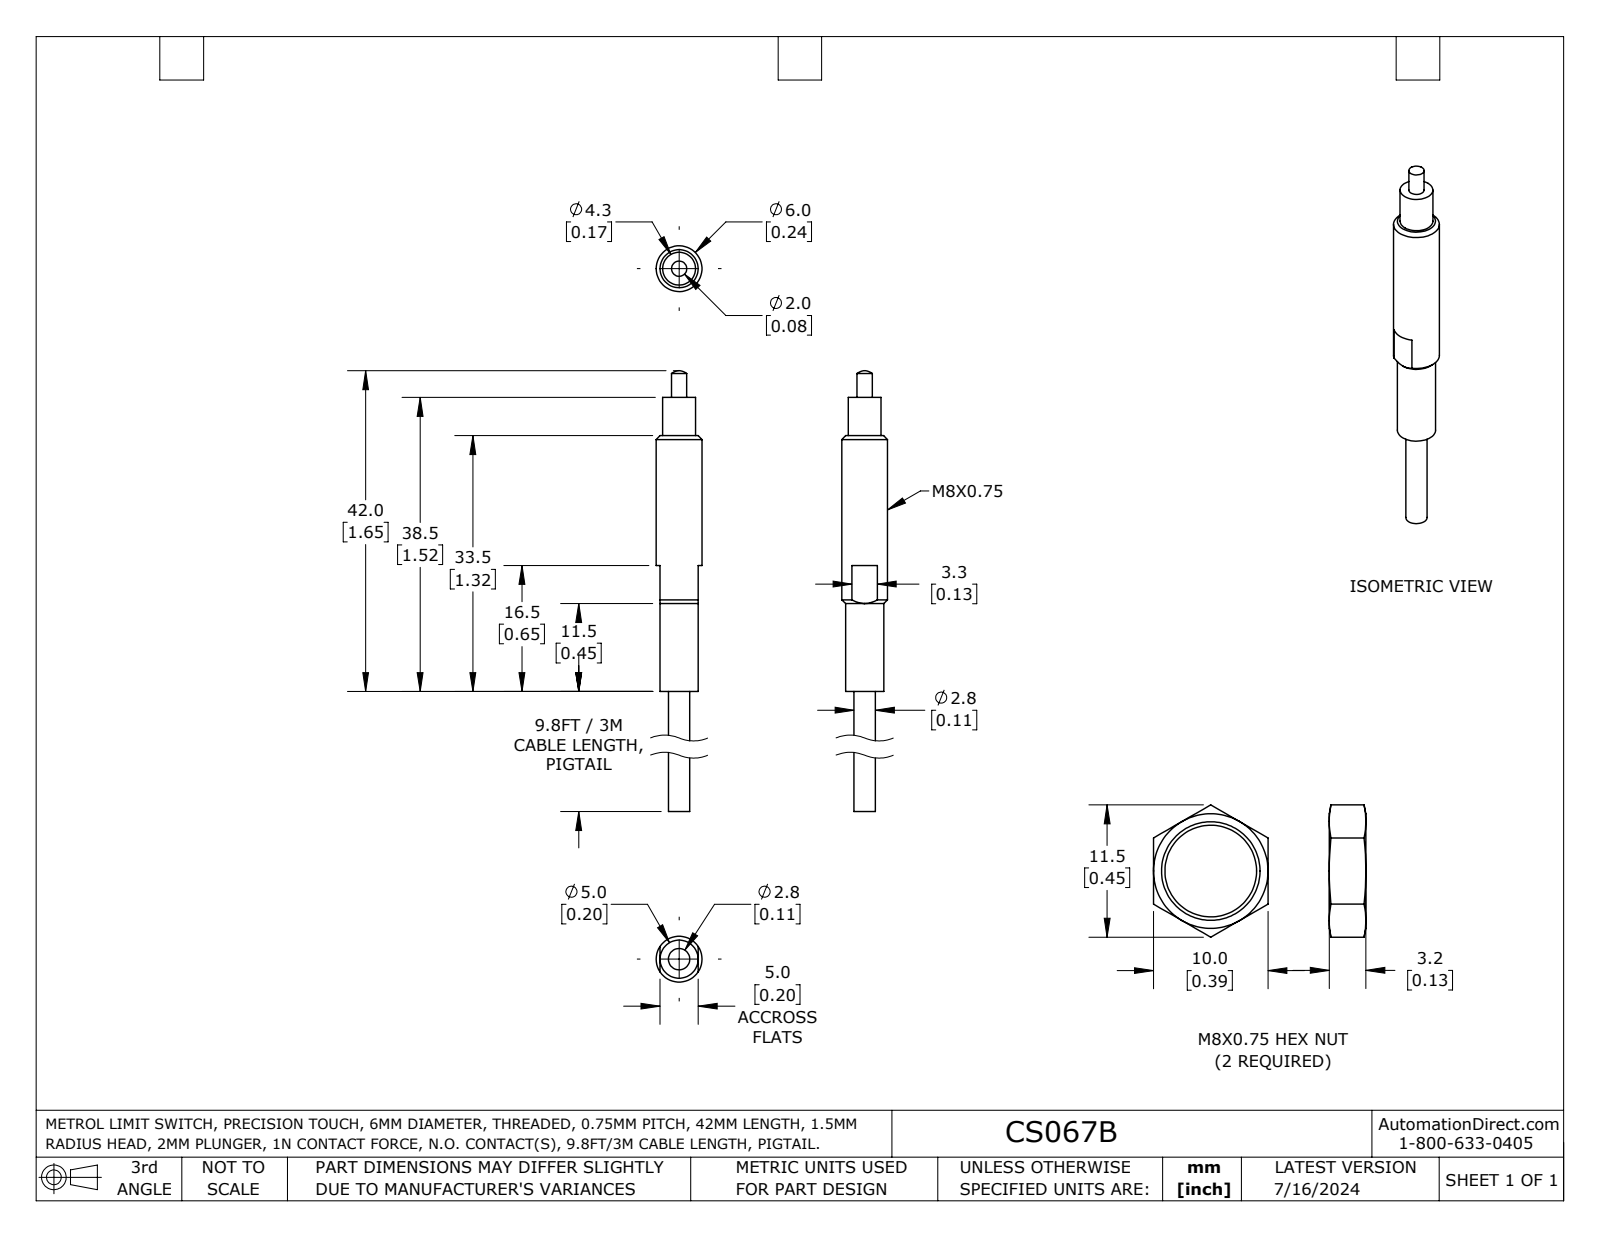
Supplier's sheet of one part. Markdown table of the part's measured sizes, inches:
| quantity | value |
| --- | --- |
| part name | CS067B |
| STEP written by | SolidWorks 2023 (AUTOMOTIVE_DESIGN) |
| units | inches |
| bodies | 1 solid, 17 faces (8 planar, 5 cylindrical, 4 other) |
| overall size | 2.205 × 0.236 × 0.236 |
| volume | 0.061 in³ |
| surface area | 1.318 in² |
| round bosses / shafts (diameter × count) | 0.236 × 1, 0.197 × 1, 0.169 × 1, 0.11 × 1, 0.079 × 1 |
| main face-to-face distances | 0.197, 1.516, 0.551, 2.067, 1.87, 1.319, 1.201, 0.65, 0.669, 0.866 |
